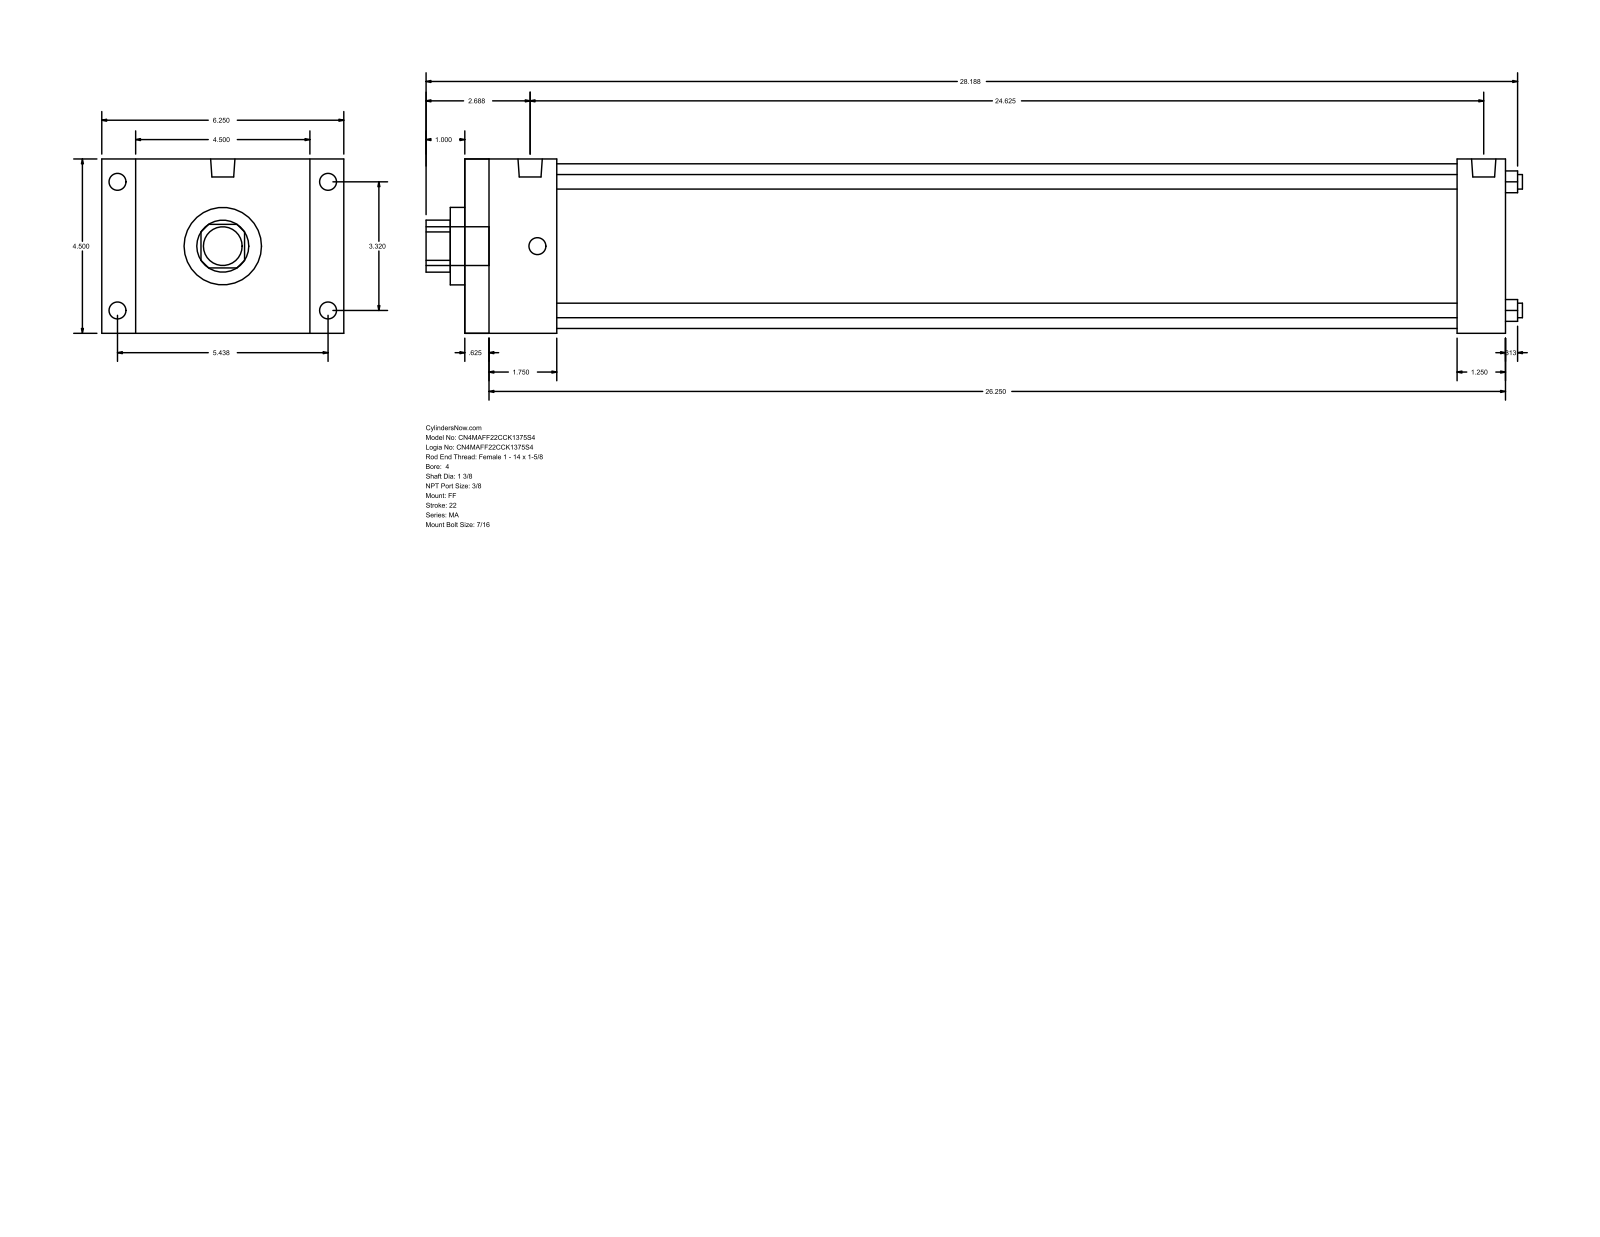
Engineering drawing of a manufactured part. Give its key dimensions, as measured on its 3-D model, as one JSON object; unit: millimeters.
{"part_name": "MA_FF__0400_1.375", "step_written_by": "GSSL Pune (CONFIG_CONTROL_DESIGN)", "units": "millimeters", "bodies": {"solids": 0, "faces": 92, "planar": 64, "cylindrical": 28, "other": 0}, "overall_size": [719.14, 158.75, 114.3], "round_holes": [[9.53, 4], [34.92, 1], [50.8, 1], [107.95, 1]], "round_bosses_or_shafts": [[11.11, 8], [15.93, 2], [25.4, 1]], "partial_cylinders_radius": [[17.06, 1]], "face_to_face_distances": [114.3, 682.62, 15.87, 666.75, 22.23, 136.53, 650.87, 635, 31.75, 60.32], "hole_center_spacings": [59.62, 84.32, 119.25]}
